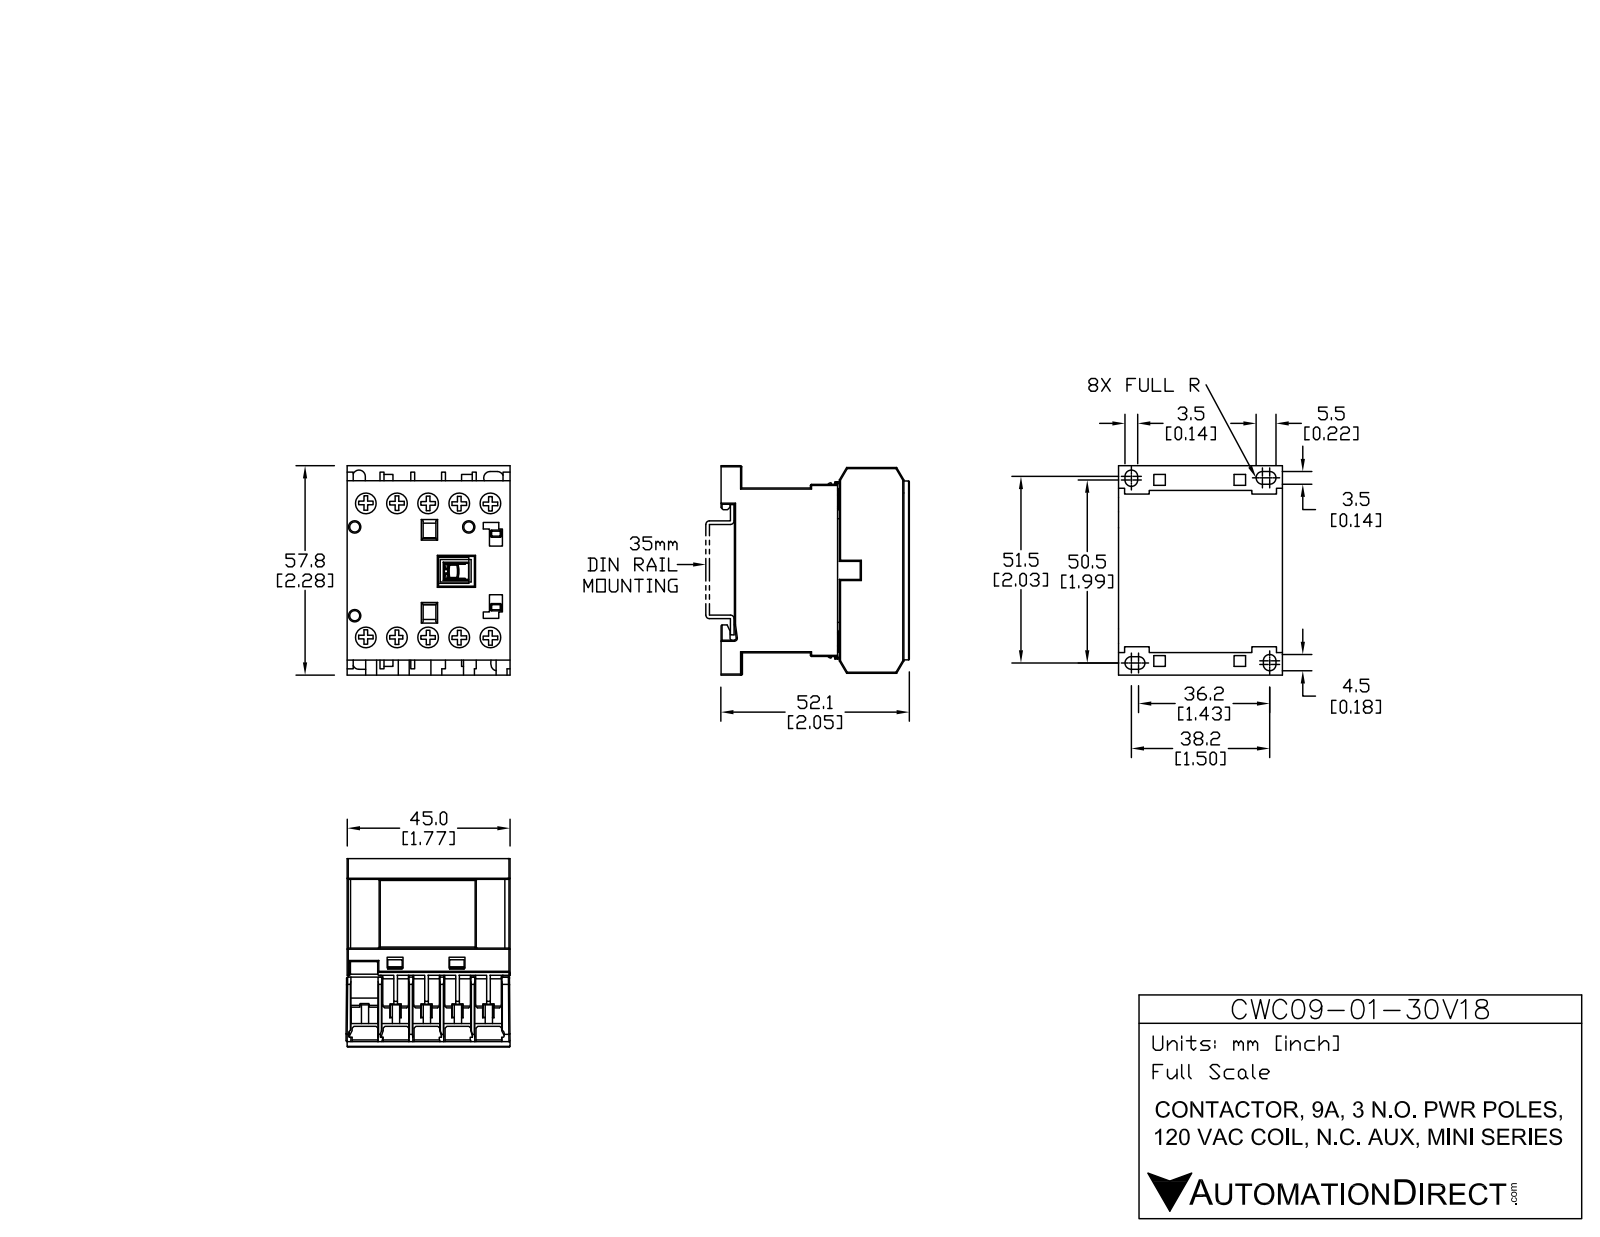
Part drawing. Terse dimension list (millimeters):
name: CWC09-01-30V18
written by: SolidWorks 2013 (AUTOMOTIVE_DESIGN)
unit: mm
bodies: 15 solids, 535 faces (445 planar, 90 cylindrical, 0 other)
size: 58.04 × 52.12 × 45.75
volume: 97 133 mm³; area: 30 437 mm²
holes: 10× ⌀6.2, 3× ⌀2.8
bosses: 10× ⌀5.9
rounds: 20× R0.3, 6× R1.72, 2× R1.73, 1× R0.32, 1× R0.42, 1× R0.55
face distances: 8.25, 45.5, 1.25, 16.5, 9.5, 5.5, 17.75, 5.13, 10.63, 7
hole spacings: 8.55, 37.94, 17.1, 40.72, 36.96, 25.65, 44.99, 6.91
